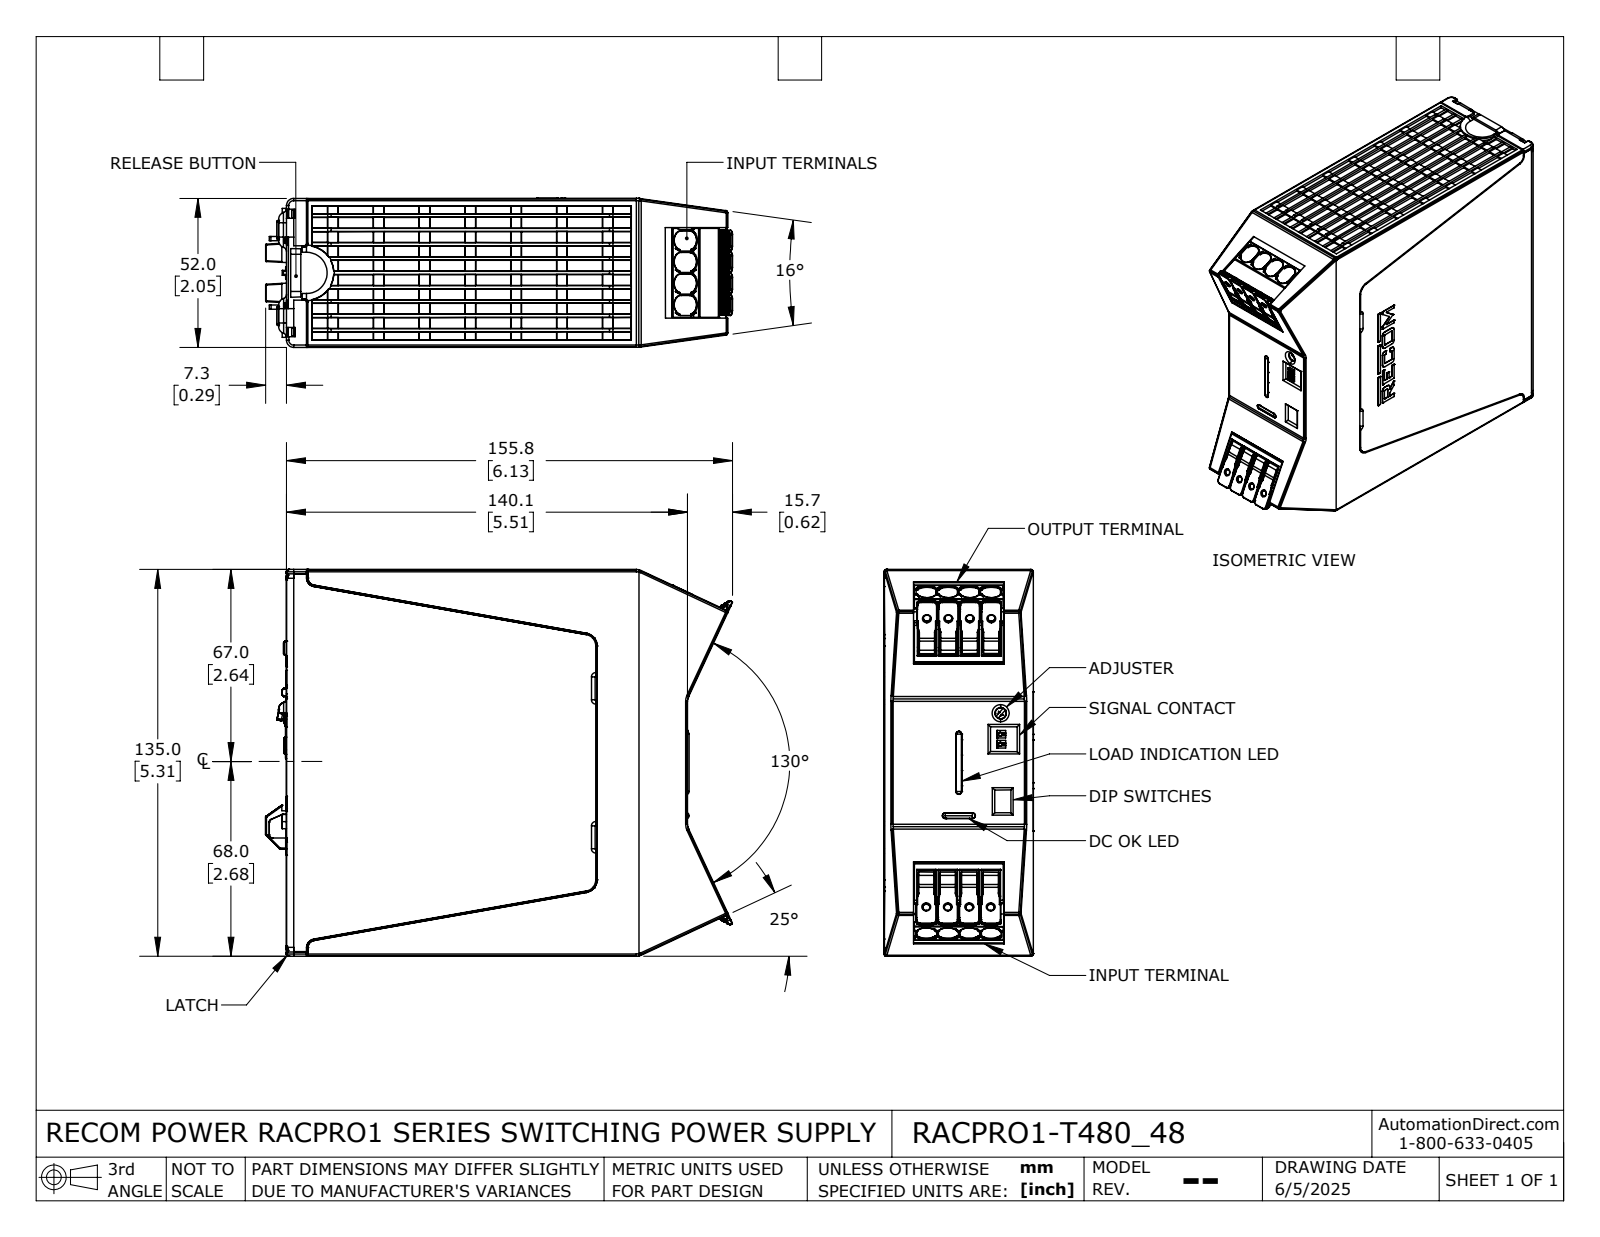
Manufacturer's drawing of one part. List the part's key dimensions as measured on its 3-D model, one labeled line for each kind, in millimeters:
Part name (STEP PRODUCT): RACPRO1-T480_48
STEP written by: SolidWorks 2024 (AUTOMOTIVE_DESIGN)
Units: millimetres
Bodies: 1 solid, 3646 faces (1958 planar, 939 cylindrical, 749 other)
Overall size (bounding box): 163 × 135 × 52
Volume: 985 500 mm³ · Surface area: 99 160 mm²
Round holes (diameter × count): ⌀2.5 ×8, ⌀2 ×2, ⌀4 ×1, ⌀4.7 ×1
Round bosses / shafts (diameter × count): ⌀5 ×2, ⌀3.8 ×1
Partial cylindrical surfaces — rounded edges, fillets, slot ends (radius × count): R0.2 ×213, R1 ×59, R2.5 ×39, R0.3 ×33, R0.5 ×31, R3 ×25, R0.8 ×23, R1.5 ×22
Main face-to-face distances: 52, 1.5, 50.5, 133.1, 5, 10, 0.5, 14.9, 134.5, 19.9
Hole centre spacings: 7.5, 15, 22.5, 38.2, 40, 51.3
